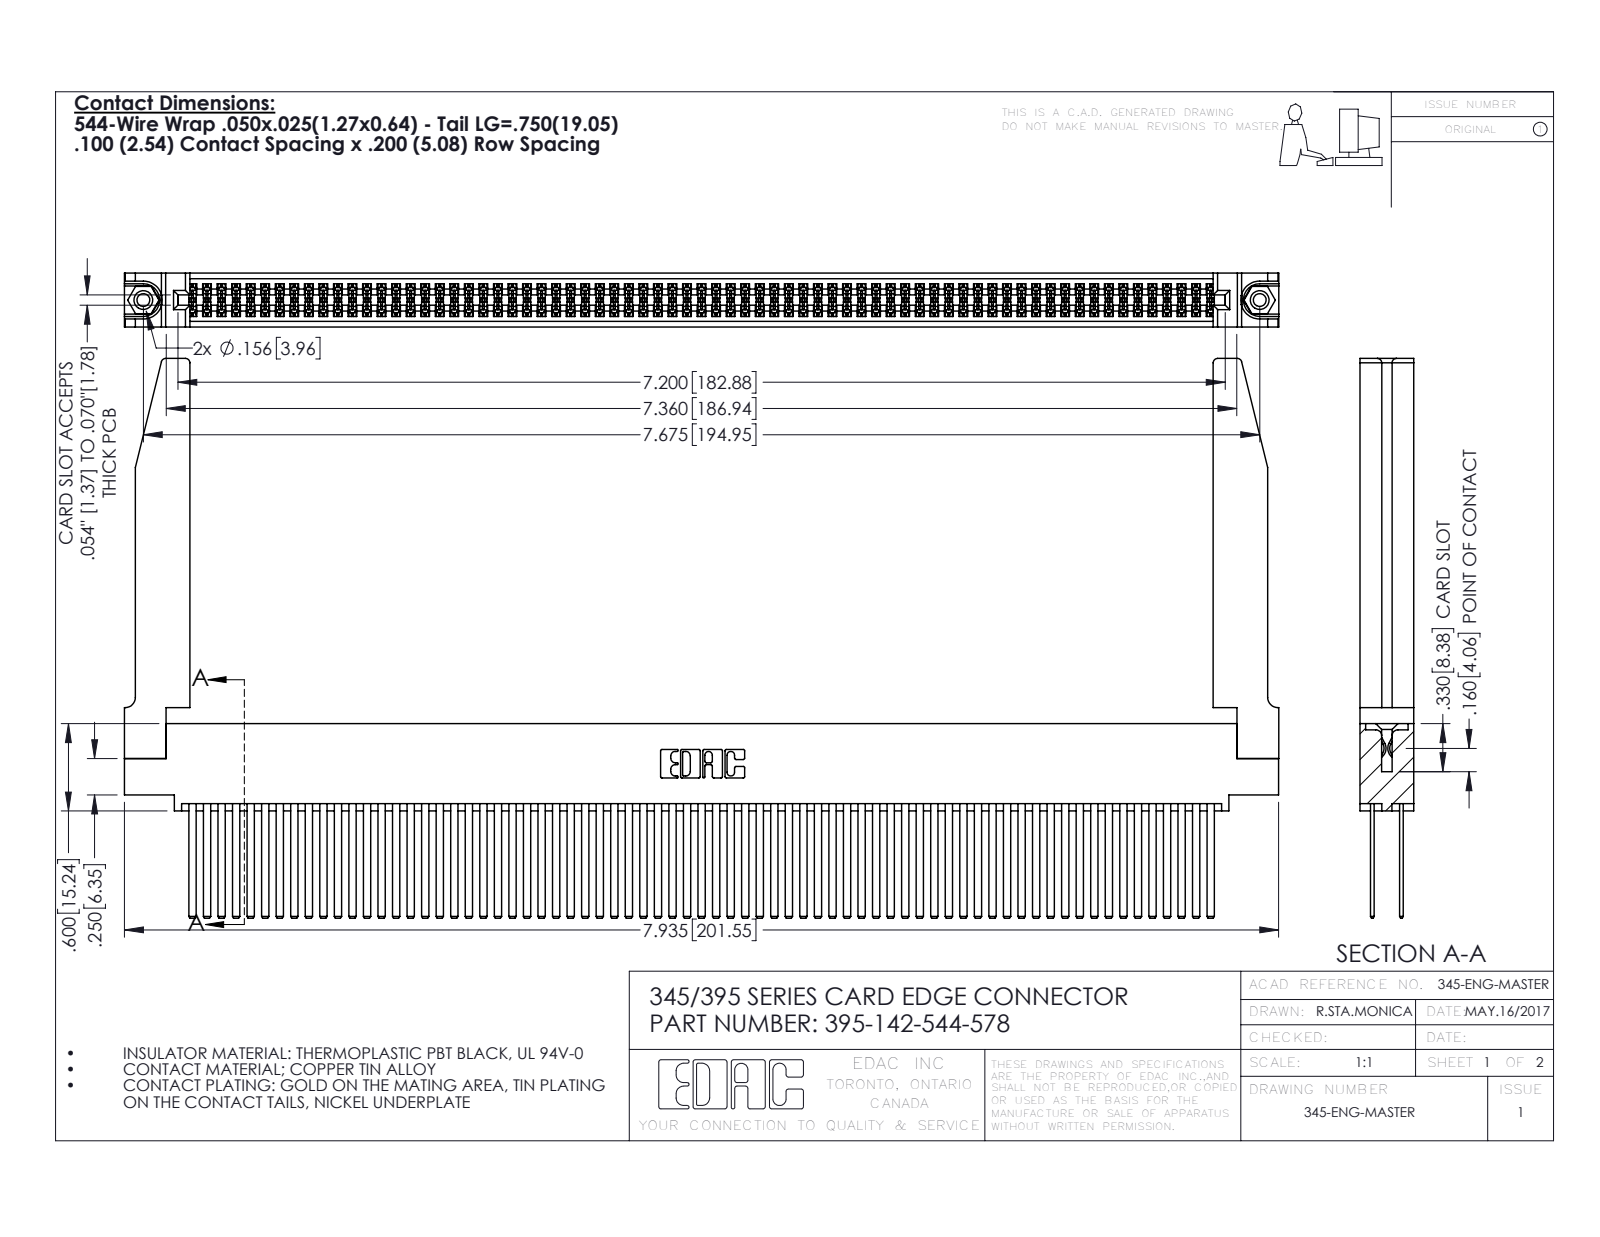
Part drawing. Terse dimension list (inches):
name: 345-292-001_345-293-144; 345-250-001_345-250-001-102; 345 Part_0.110 Offset - 0.156 Dia-TH; 395-142-544-578 (+1 more)
written by: SolidWorks 2016 (CONFIG_CONTROL_DESIGN)
unit: in
bodies: 147 solids, 6612 faces (4344 planar, 2216 cylindrical, 52 other)
size: 7.936 × 3.847 × 0.37
volume: 1.803 in³; area: 70.53 in²
holes: 2× ⌀0.089, 2× ⌀0.125, 2× ⌀0.156, 1× ⌀0.064
bosses: 2× ⌀0.155
rounds: 213× R0.006, 22× R0.01, 8× R0.03, 6× R0.007, 6× R0.031, 3× R0.026, 2× R0.014, 2× R0.019
face distances: 0.072, 0.298, 0.098, 0.272, 0.025, 0.2, 0.37, 0.225, 0.175, 0.149
hole spacings: 0.27, 7.439, 7.675
